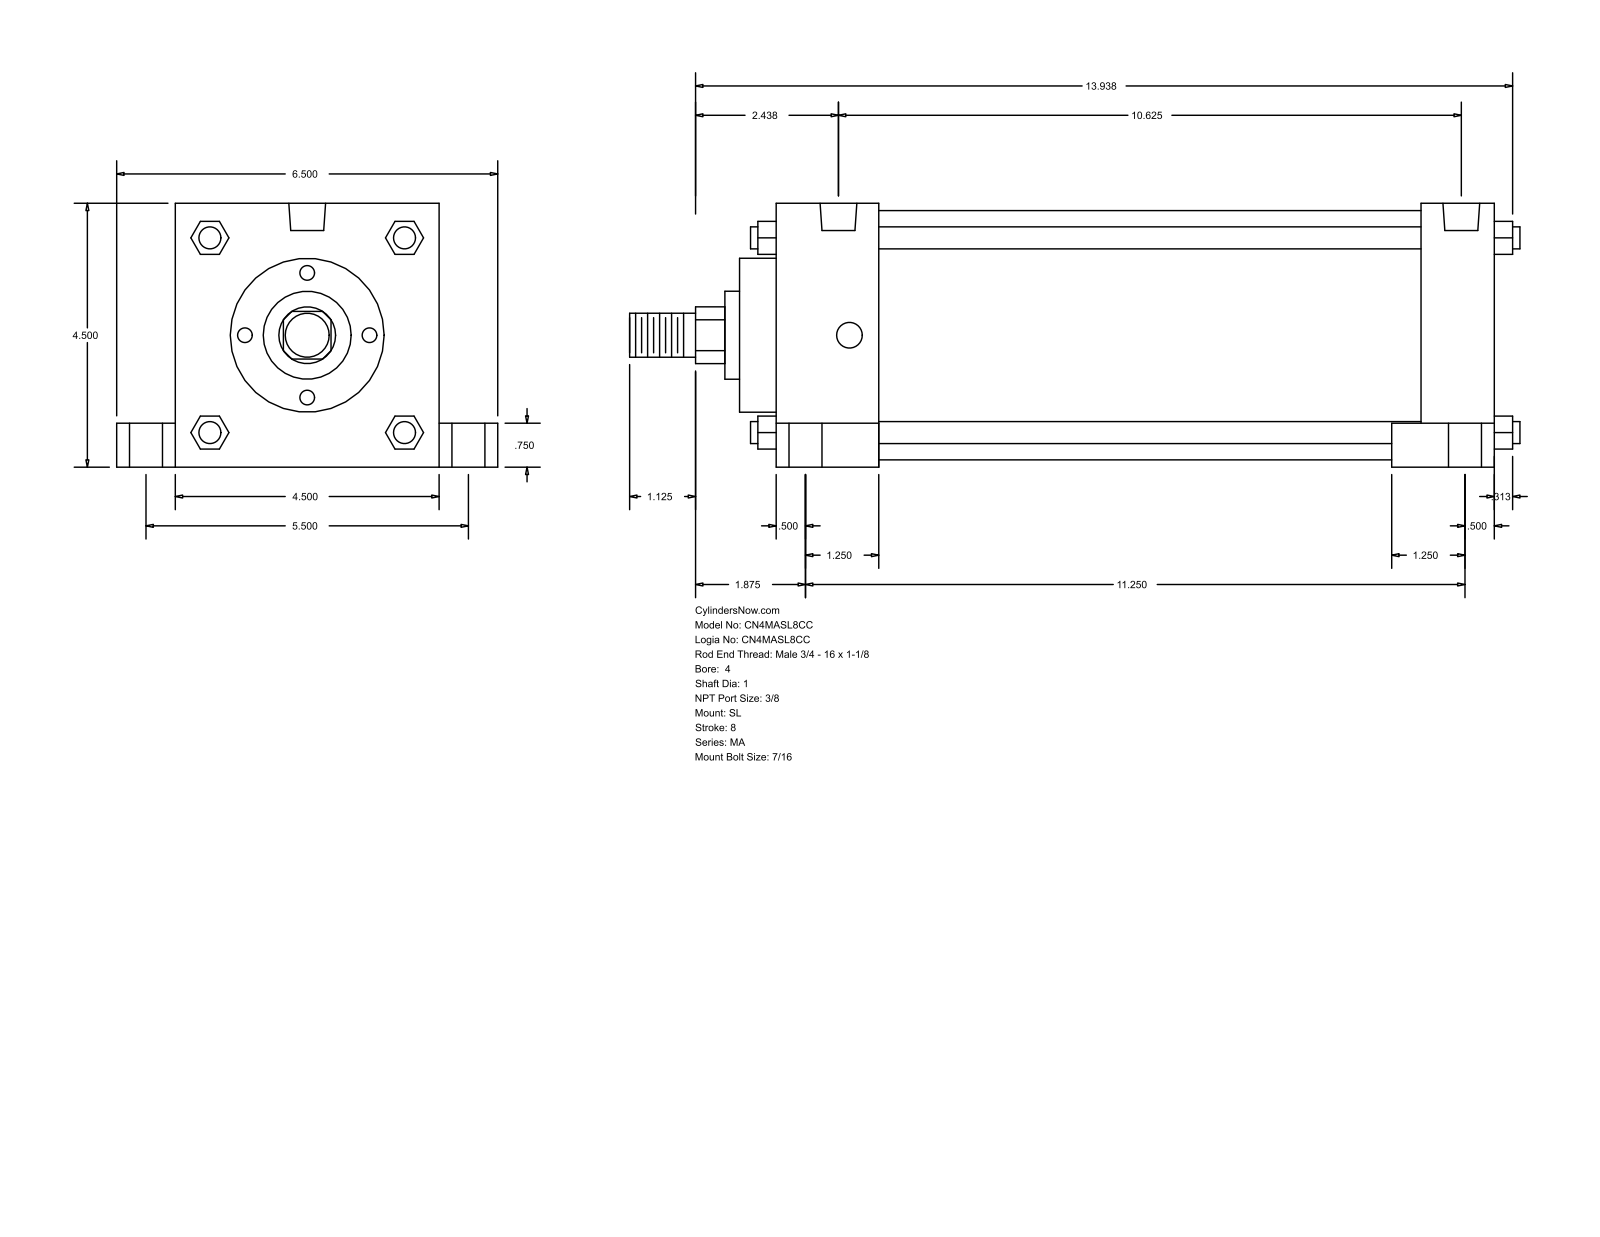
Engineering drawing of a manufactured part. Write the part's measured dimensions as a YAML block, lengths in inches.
part_name: "MA_SL__0400_1"
step_written_by: "GSSL Pune (CONFIG_CONTROL_DESIGN)"
units: inches
bodies: {solids: 0, faces: 150, planar: 113, cylindrical: 37, other: 0}
overall_size: [15.187, 6.5, 4.5]
round_holes:
  - {diameter: 0.437, count: 4}
  - {diameter: 0.563, count: 4}
  - {diameter: 0.813, count: 4}
  - {diameter: 0.627, count: 2}
round_bosses_or_shafts:
  - {diameter: 0.375, count: 4}
  - {diameter: 4.25, count: 1}
  - {diameter: 2.625, count: 1}
  - {diameter: 1.5, count: 1}
  - {diameter: 1, count: 1}
  - {diameter: 0.75, count: 1}
partial_cylinders:
  - {radius: 0.484, count: 1}
face_to_face_distances: [4.5, 12.25, 1.75, 10.5, 11, 9.25, 1.25, 1, 5.5, 12.875]
hole_center_spacings: [2.751, 2.761, 2.807, 2.85, 5.5, 10.25, 10.854, 11.036]
